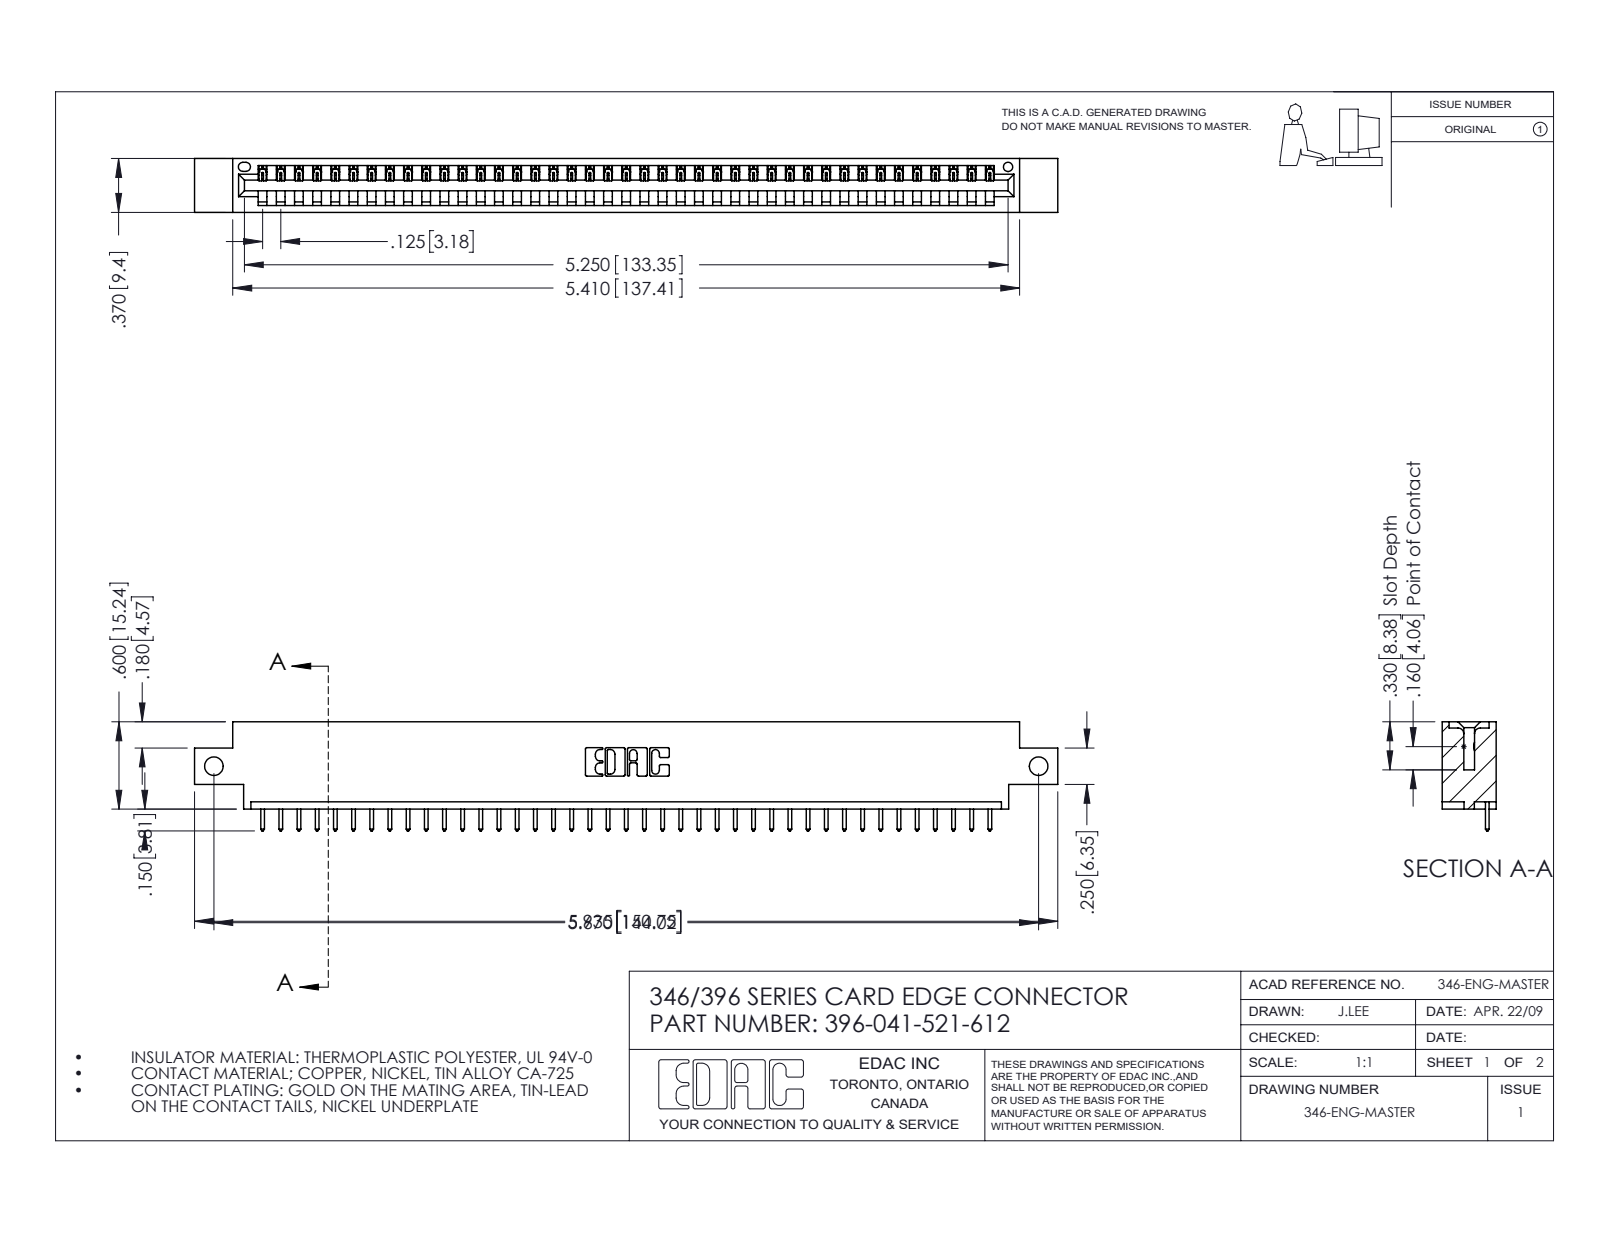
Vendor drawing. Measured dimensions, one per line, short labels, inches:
name: 345-292-001_345-293-121; 346 Part_0.170 Offset - Side Mount; 396-041-521-612
written by: SolidWorks 2016 (CONFIG_CONTROL_DESIGN)
unit: in
bodies: 42 solids, 2504 faces (1720 planar, 784 cylindrical, 0 other)
size: 5.935 × 0.75 × 0.37
volume: 0.858 in³; area: 26.53 in²
holes: 2× ⌀0.128, 1× ⌀0.064
rounds: 82× R0.006, 82× R0.01, 22× R0.01, 6× R0.007, 6× R0.031, 3× R0.026, 2× R0.031, 2× R0.04
face distances: 0.048, 0.322, 0.37, 0.25, 0.072, 0.298, 0.025, 0.148, 0.222, 0.1
hole spacings: 5.67
